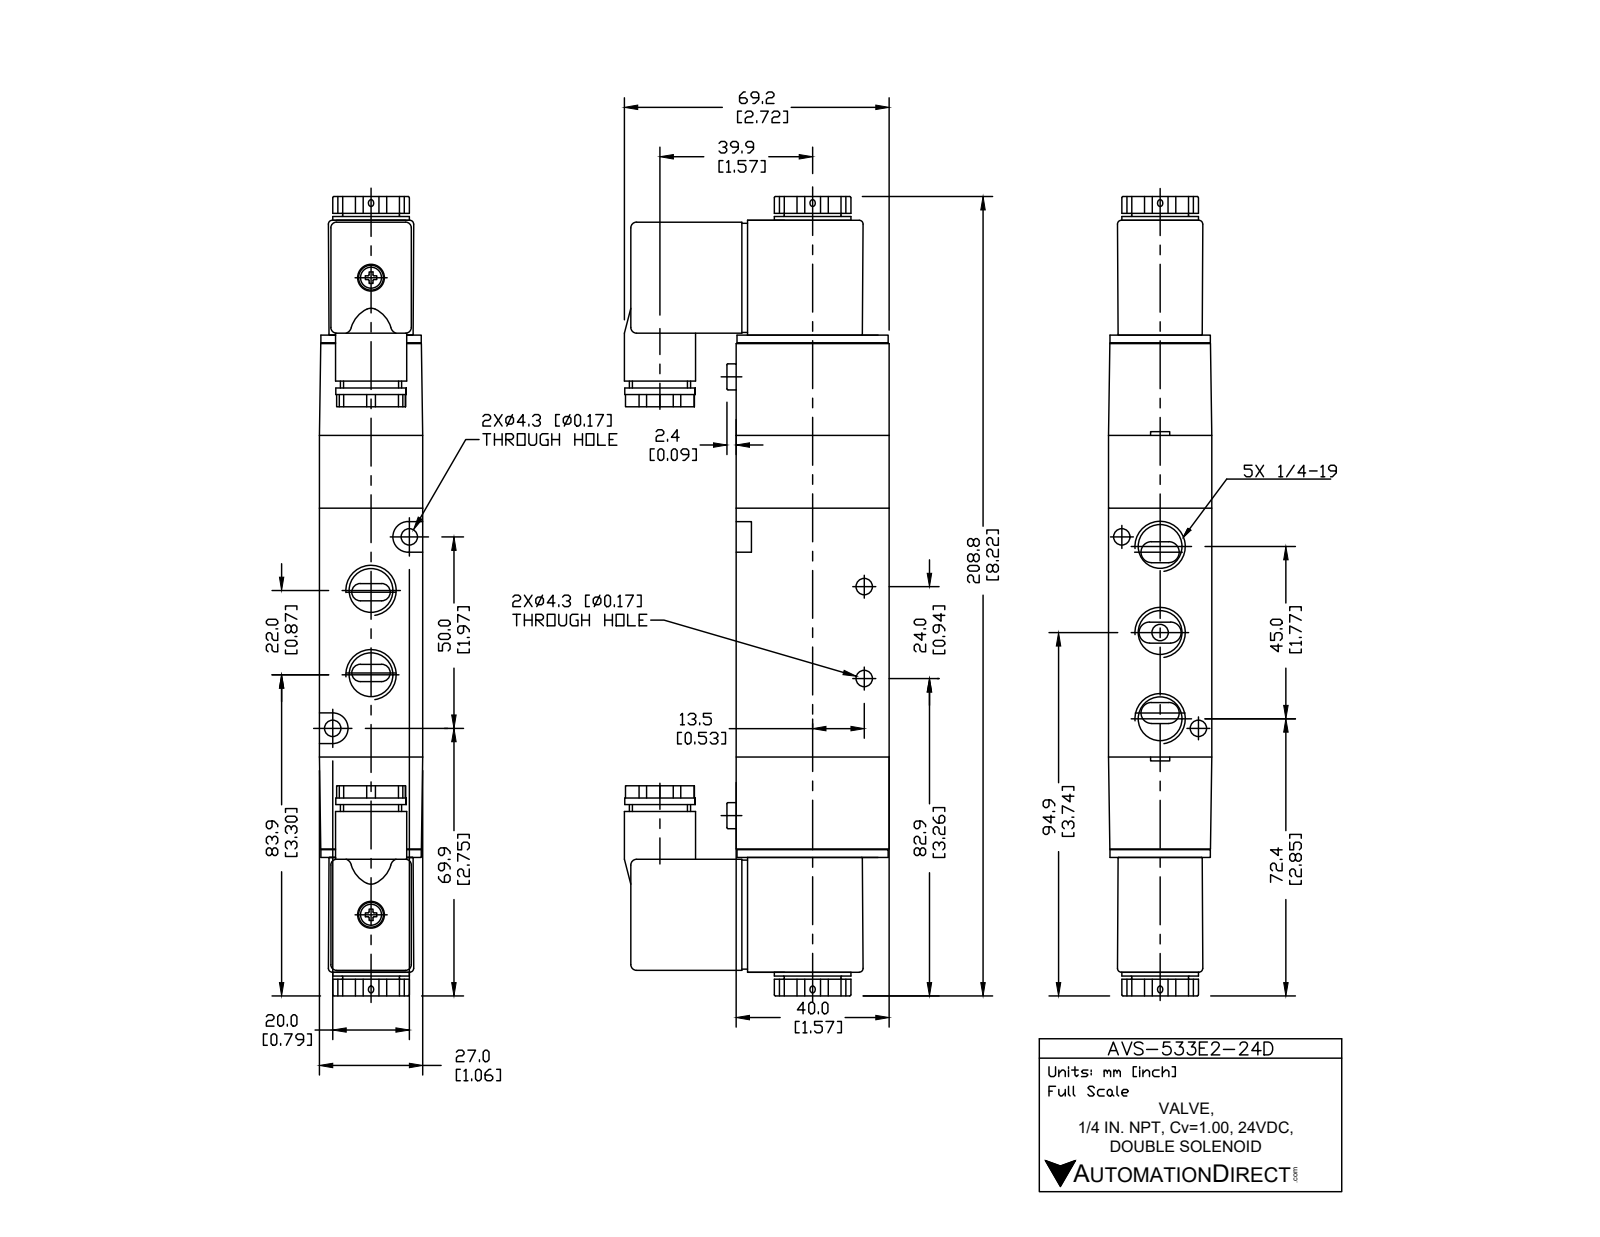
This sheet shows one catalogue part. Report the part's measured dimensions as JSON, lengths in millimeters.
{"part_name": "AVS-533E2-24D", "step_written_by": "SolidWorks 2015 (CONFIG_CONTROL_DESIGN)", "units": "millimeters", "bodies": {"solids": 5, "faces": 278, "planar": 133, "cylindrical": 111, "other": 34}, "overall_size": [208.8, 69.2, 27], "volume_mm3": 224505, "surface_area_mm2": 45623, "round_holes": [[11.13, 5], [4.3, 4], [9.3, 1]], "round_bosses_or_shafts": [[6.7, 2], [20, 1], [18.6, 1], [18.4, 1], [16, 1], [14.8, 1]], "partial_cylinders_radius": [[1.5, 18], [3, 12], [1, 10], [0.5, 8]], "face_to_face_distances": [27, 3, 24, 40, 84, 23.22, 21, 29.5, 0.5, 166.4], "hole_center_spacings": [10.31, 11, 11.5, 17.2, 22.5, 26.93, 33.5, 37.36]}
